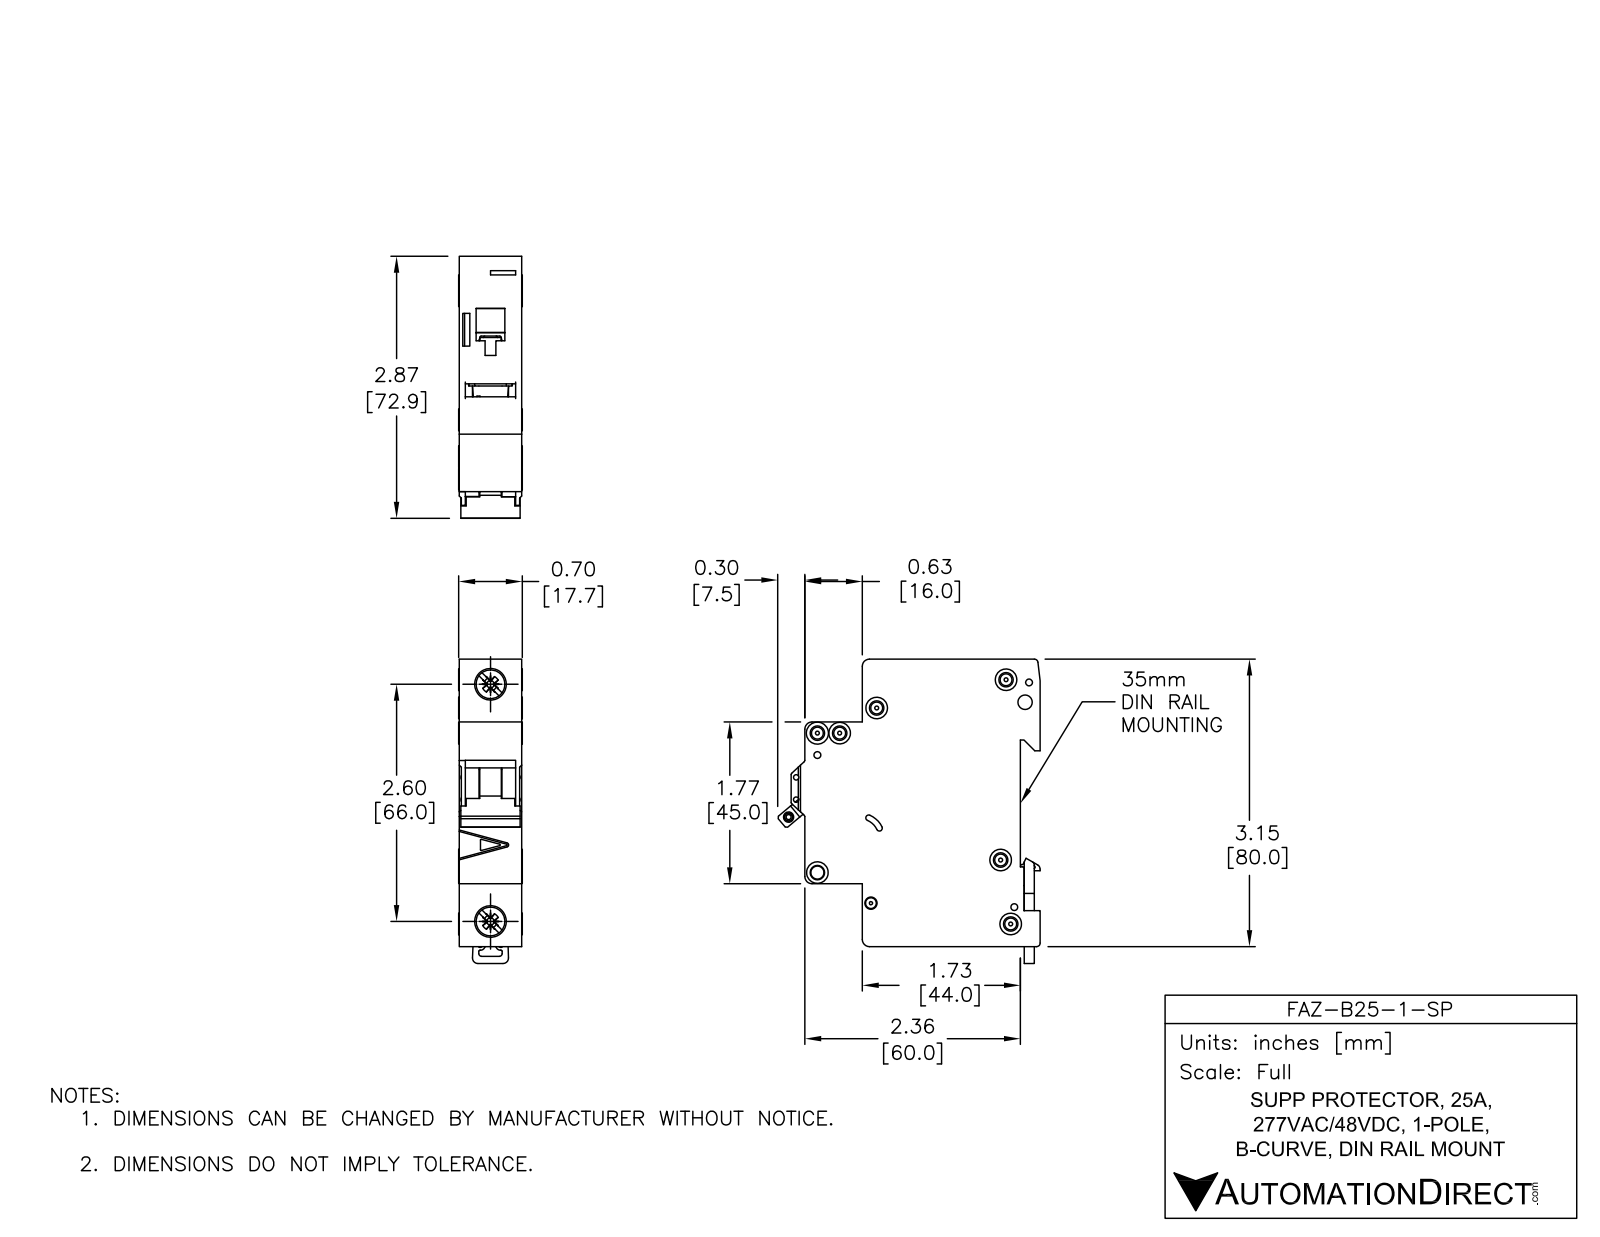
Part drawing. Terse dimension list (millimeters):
name: FAZ-B25-1-SP
written by: SolidWorks 2014 (AUTOMOTIVE_DESIGN)
unit: mm
bodies: 5 solids, 558 faces (235 planar, 202 cylindrical, 121 other)
size: 84.78 × 73.04 × 17.7
volume: 74 935 mm³; area: 19 545 mm²
holes: 6× ⌀3.6, 3× ⌀1.9, 2× ⌀1.09, 2× ⌀1.5, 2× ⌀4, 2× ⌀7.15, 1× ⌀2.15, 1× ⌀2.2, 1× ⌀2.55, 1× ⌀3.3, 1× ⌀3.4
bosses: 4× ⌀6, 2× ⌀8.2, 1× ⌀2.5
rounds: 30× R0.25, 13× R0.5, 8× R2, 5× R0.2, 4× R1, 2× R0.8, 2× R3, 1× R1.5
face distances: 17.5, 79.48, 5.5, 49.5, 44, 65.5, 60, 16, 1.75, 15.75
hole spacings: 6.2, 13.64, 4.81, 5.19, 5.61, 6.1, 6.44, 8.19
